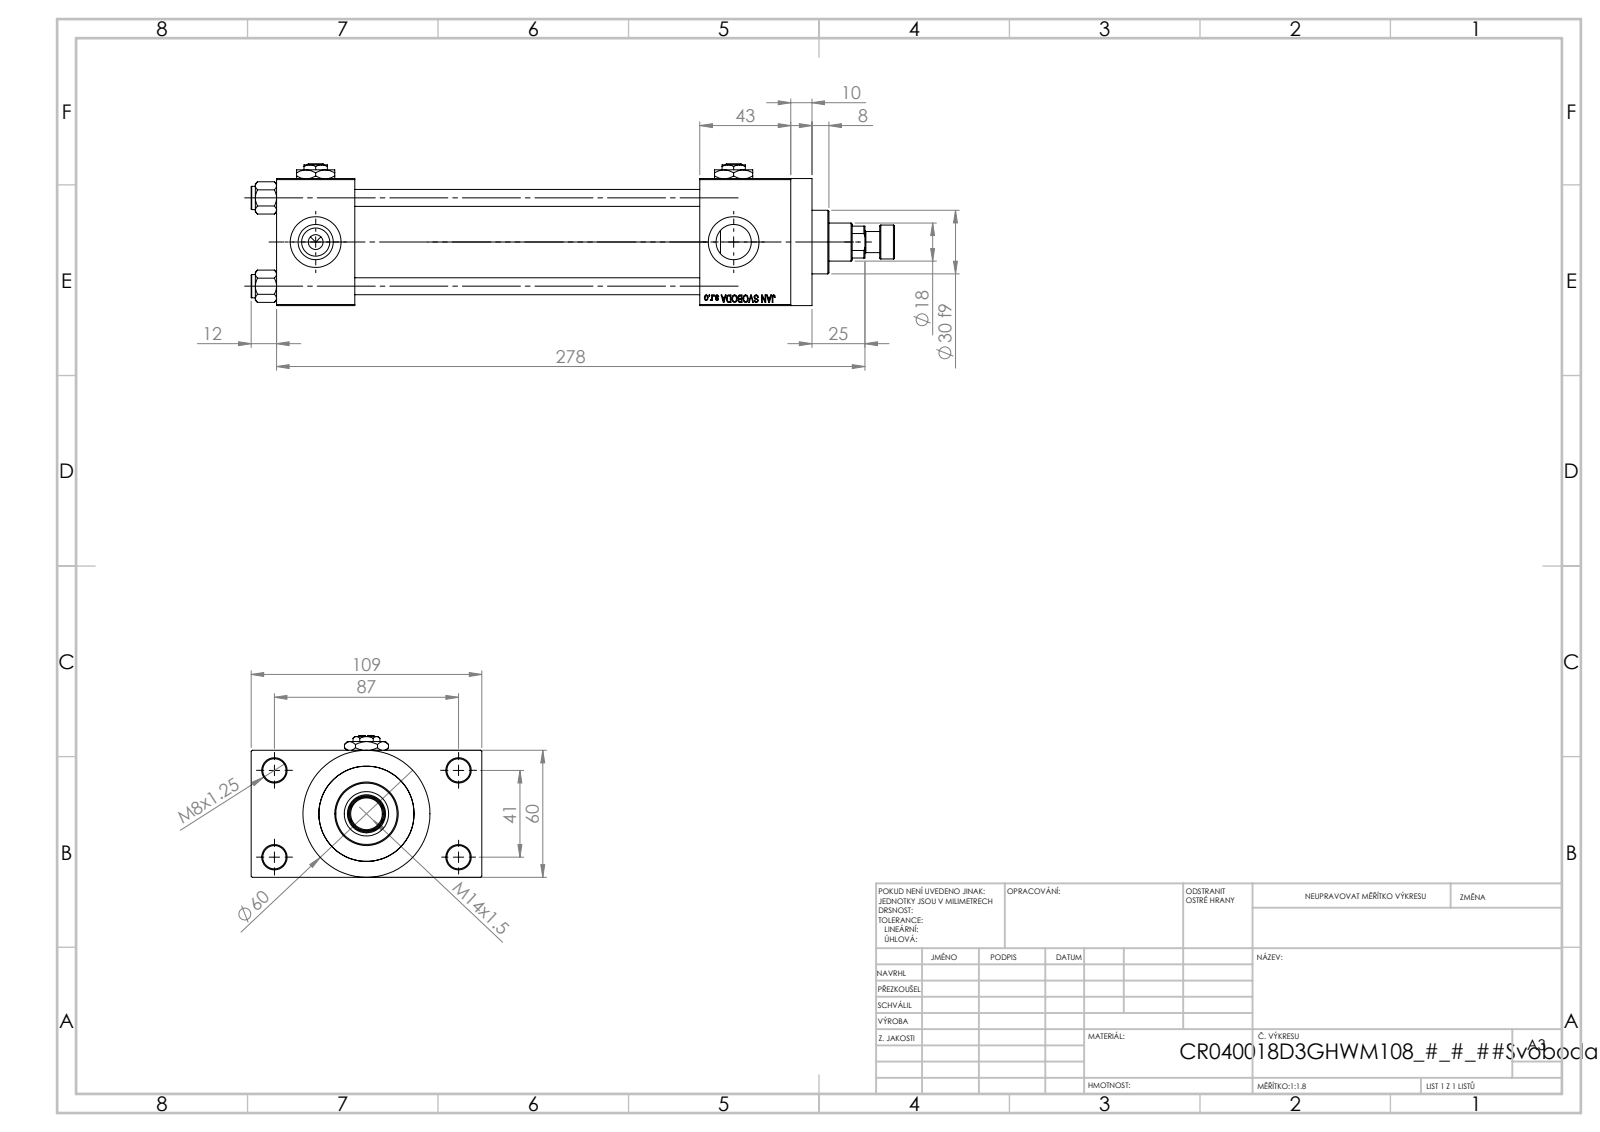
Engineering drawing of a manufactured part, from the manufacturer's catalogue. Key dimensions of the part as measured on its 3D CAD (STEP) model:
Part name (STEP PRODUCT): Zatka_pro_OIL_PORT; V215CR_D_Body; V215CR_VCP_D; NUT_M5_D (+3 more)
STEP written by: SolidWorks 2019 (CONFIG_CONTROL_DESIGN)
Units: millimetres
Bodies: 14 solids, 1218 faces (549 planar, 103 cylindrical, 566 other)
Overall size (bounding box): 304 × 109 × 67
Volume: 602 677 mm³ · Surface area: 171 030 mm²
Round holes (diameter × count): ⌀8 ×4, ⌀11 ×4, ⌀16.66 ×4, ⌀24 ×4, ⌀7 ×3, ⌀8.5 ×1, ⌀18 ×1, ⌀21 ×1, ⌀31 ×1, ⌀40 ×1, ⌀45 ×1
Round bosses / shafts (diameter × count): ⌀11 ×4, ⌀60 ×1, ⌀46 ×1, ⌀30 ×1, ⌀16 ×1, ⌀10 ×1
Partial cylindrical surfaces — rounded edges, fillets, slot ends (radius × count): R8.5 ×1
Main face-to-face distances: 60, 24.5, 163, 84.5, 37, 200, 43, 243, 206, 10
Hole centre spacings: 22.65, 29.49, 41.7, 47.15, 48.09, 64.35, 76.49, 41
